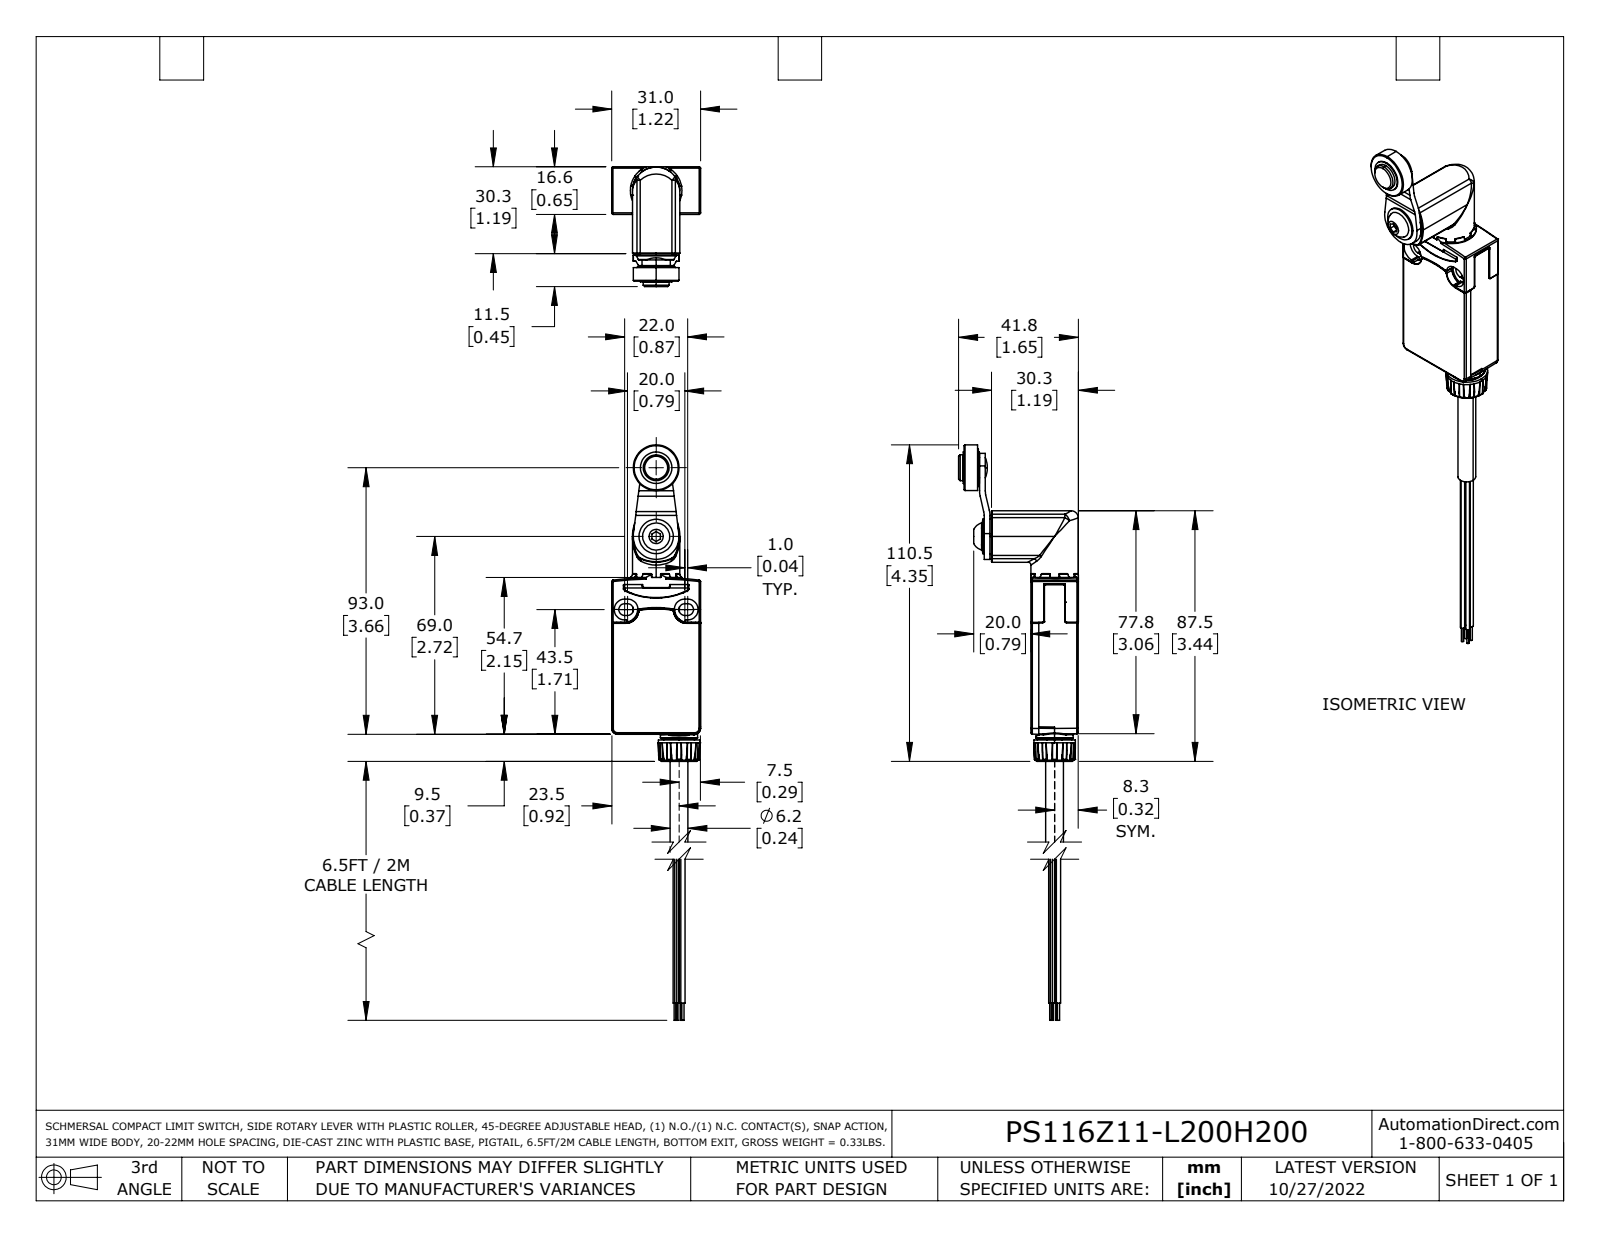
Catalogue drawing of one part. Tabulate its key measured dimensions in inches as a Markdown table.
| quantity | value |
| --- | --- |
| part name | PS116Z11-L200H200_Default |
| STEP written by | SolidWorks 2021 (CONFIG_CONTROL_DESIGN) |
| units | inches |
| bodies | 1 solid, 1082 faces (335 planar, 442 cylindrical, 305 other) |
| overall size | 8.602 × 1.646 × 1.22 |
| volume | 2.425 in³ |
| surface area | 27.85 in² |
| round holes (diameter × count) | 0.48 × 2, 0.079 × 1, 0.252 × 1, 0.571 × 1, 0.583 × 1 |
| round bosses / shafts (diameter × count) | 0.059 × 4, 0.031 × 4, 0.512 × 2, 0.65 × 1, 0.63 × 1, 0.571 × 1, 0.567 × 1, 0.524 × 1 |
| partial cylindrical surfaces (radius × count) | 0.008 × 134, 0.004 × 61, 0.02 × 30, 0.014 × 10, 0.039 × 8, 0.012 × 6, 0.079 × 5, 0.081 × 4 |
| main face-to-face distances | 0.65, 0.652, 0.079, 1.22, 0.063, 0.118, 0.654, 0.016, 0.453, 0.291 |
| hole center spacings | 0.315 |
